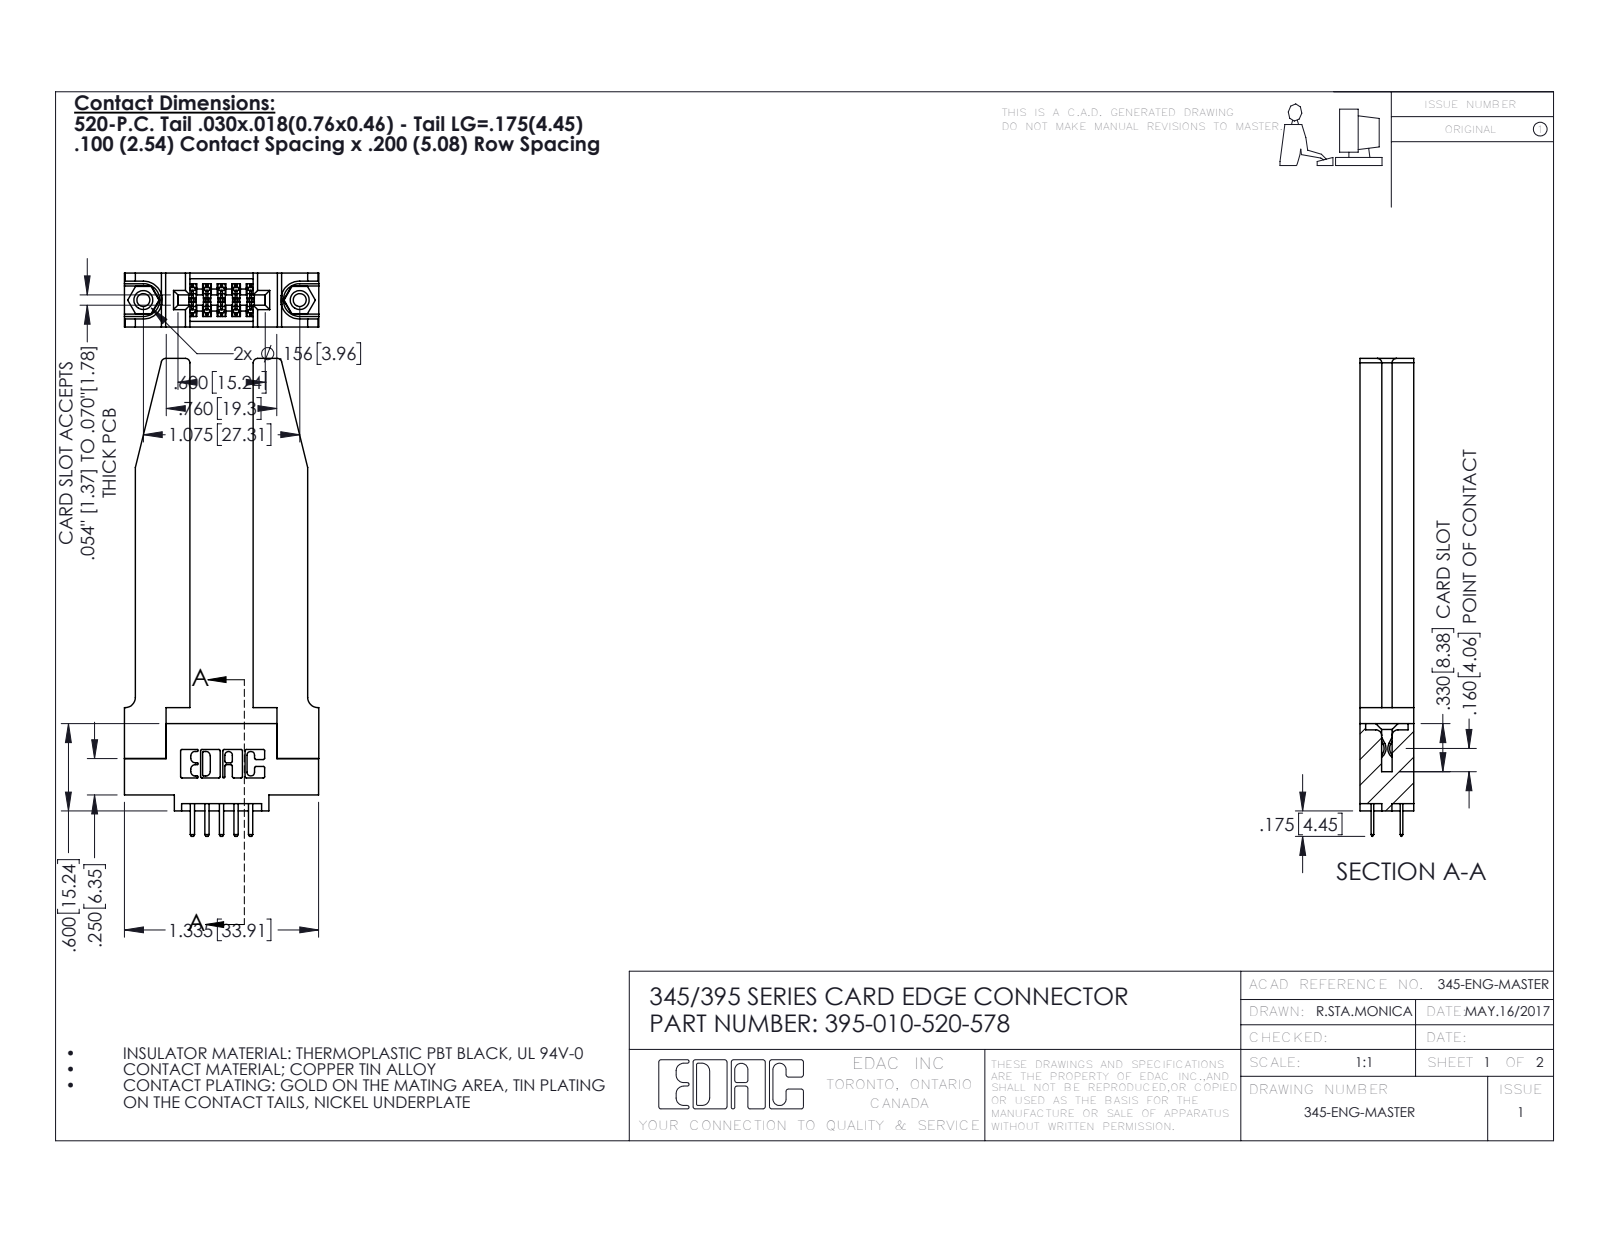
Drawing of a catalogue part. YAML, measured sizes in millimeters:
part_name: "345 Part_0.110 Offset - 0.156 Dia-TH; 345-250-001_345-250-001-102; 345-220-078_345-220-078; 395-010-520-578 (+1 more)"
step_written_by: "SolidWorks 2016 (CONFIG_CONTROL_DESIGN)"
units: millimeters
bodies: {solids: 15, faces: 904, planar: 576, cylindrical: 276, other: 52}
overall_size: [83.4, 33.9, 9.4]
volume: 10700
surface_area: 10460
round_holes:
  - {diameter: 2.3, count: 2}
  - {diameter: 3.2, count: 2}
  - {diameter: 4, count: 2}
  - {diameter: 1.6, count: 1}
round_bosses_or_shafts:
  - {diameter: 3.9, count: 2}
partial_cylinders:
  - {radius: 0.3, count: 22}
  - {radius: 0.2, count: 15}
  - {radius: 0.3, count: 14}
  - {radius: 0.8, count: 8}
  - {radius: 0.2, count: 6}
  - {radius: 0.8, count: 6}
  - {radius: 0.7, count: 3}
  - {radius: 0.4, count: 2}
face_to_face_distances: [9.4, 3.8, 5.6, 11, 1.8, 7.6, 2, 3.8, 5.1, 1.4]
hole_center_spacings: [6.9, 21.5, 27.3]
